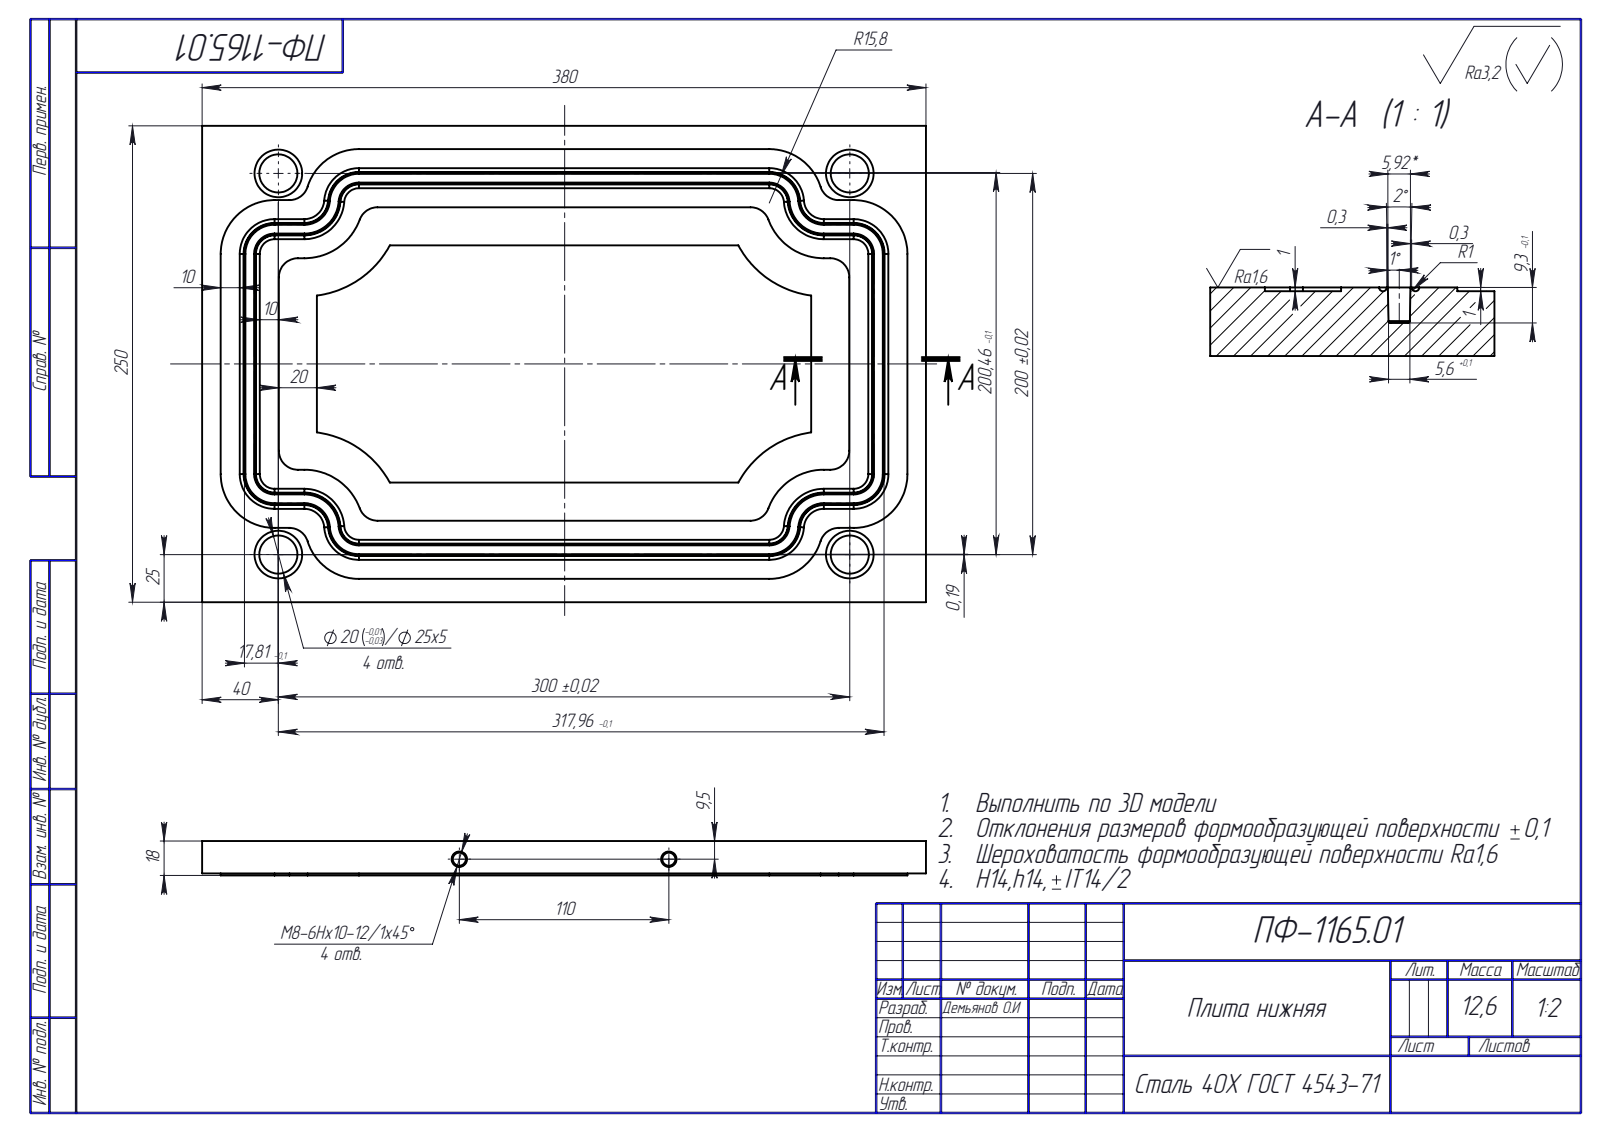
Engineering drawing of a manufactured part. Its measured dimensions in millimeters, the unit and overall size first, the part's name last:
Units: millimetres
Overall size (bounding box): 380 × 250 × 18
Round holes (diameter × count): ⌀20 ×4, ⌀25 ×4, ⌀6.8 ×2
Partial cylindrical surfaces — rounded edges, fillets, slot ends (radius × count): R0.5 ×12, R1 ×12, R10 ×12, R28.26 ×8, R30.96 ×4, R50.96 ×4
Main face-to-face distances: 18, 17, 1, 250, 8.7, 8.3, 9.3, 380, 195, 330
Hole centre spacings: 200, 300, 360.56, 110
Volume: 1 592 000 mm³ · Surface area: 237 106 mm²
Bodies: 1 solid, 225 faces (53 planar, 84 cylindrical, 88 other)
Part name (STEP PRODUCT): НЛС-ПФ-1165-01 Плита нижняя
STEP written by: SolidWorks 2012 (AUTOMOTIVE_DESIGN)
